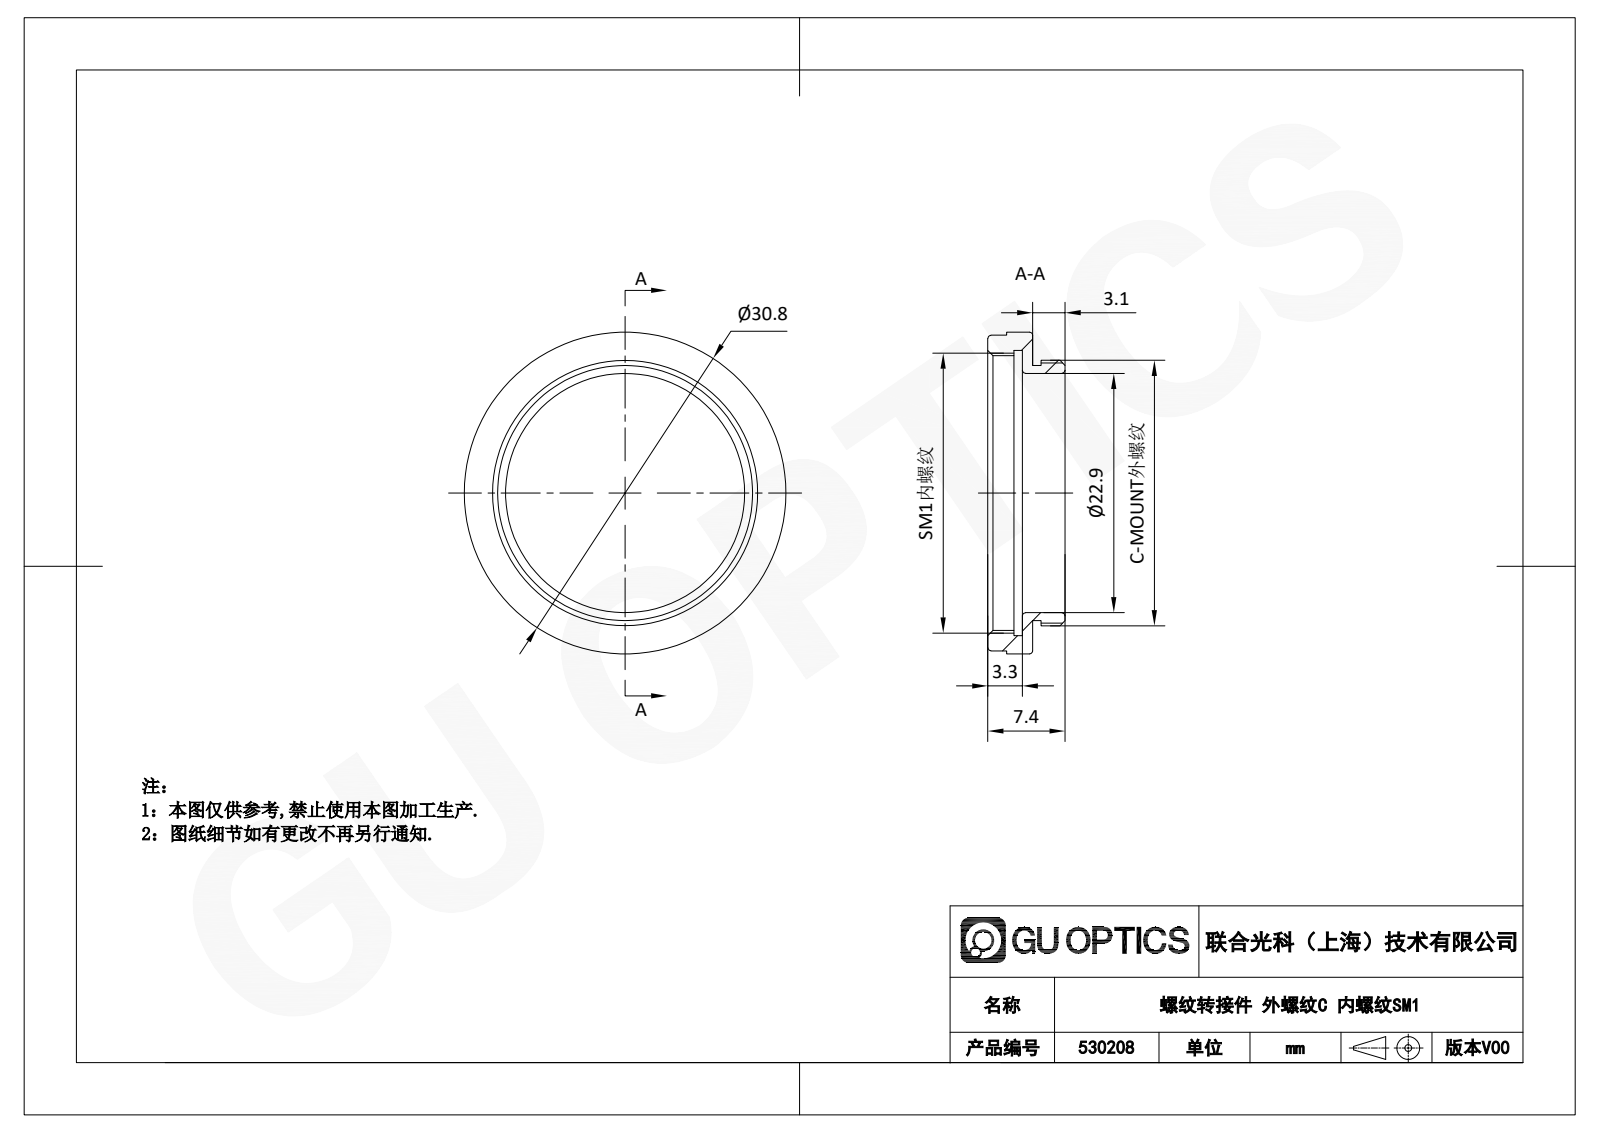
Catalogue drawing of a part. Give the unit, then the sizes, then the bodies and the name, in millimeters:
Units: millimetres
Overall size (bounding box): 30.8 × 30.8 × 7.4
Round holes (diameter × count): ⌀22.9 ×1, ⌀26.29 ×1, ⌀27.3 ×1
Round bosses / shafts (diameter × count): ⌀30.8 ×1, ⌀30.2 ×1, ⌀25.4 ×1, ⌀24.4 ×1
Main face-to-face distances: 1, 3.3, 1.8, 4.3, 0.8, 2.5, 2.6, 5.1, 2.3, 3.1
Volume: 1 151 mm³ · Surface area: 1 967 mm²
Bodies: 1 solid, 20 faces (7 planar, 7 cylindrical, 6 other)
Part name (STEP PRODUCT): 530208
STEP written by: SolidWorks 2020 (CONFIG_CONTROL_DESIGN)
